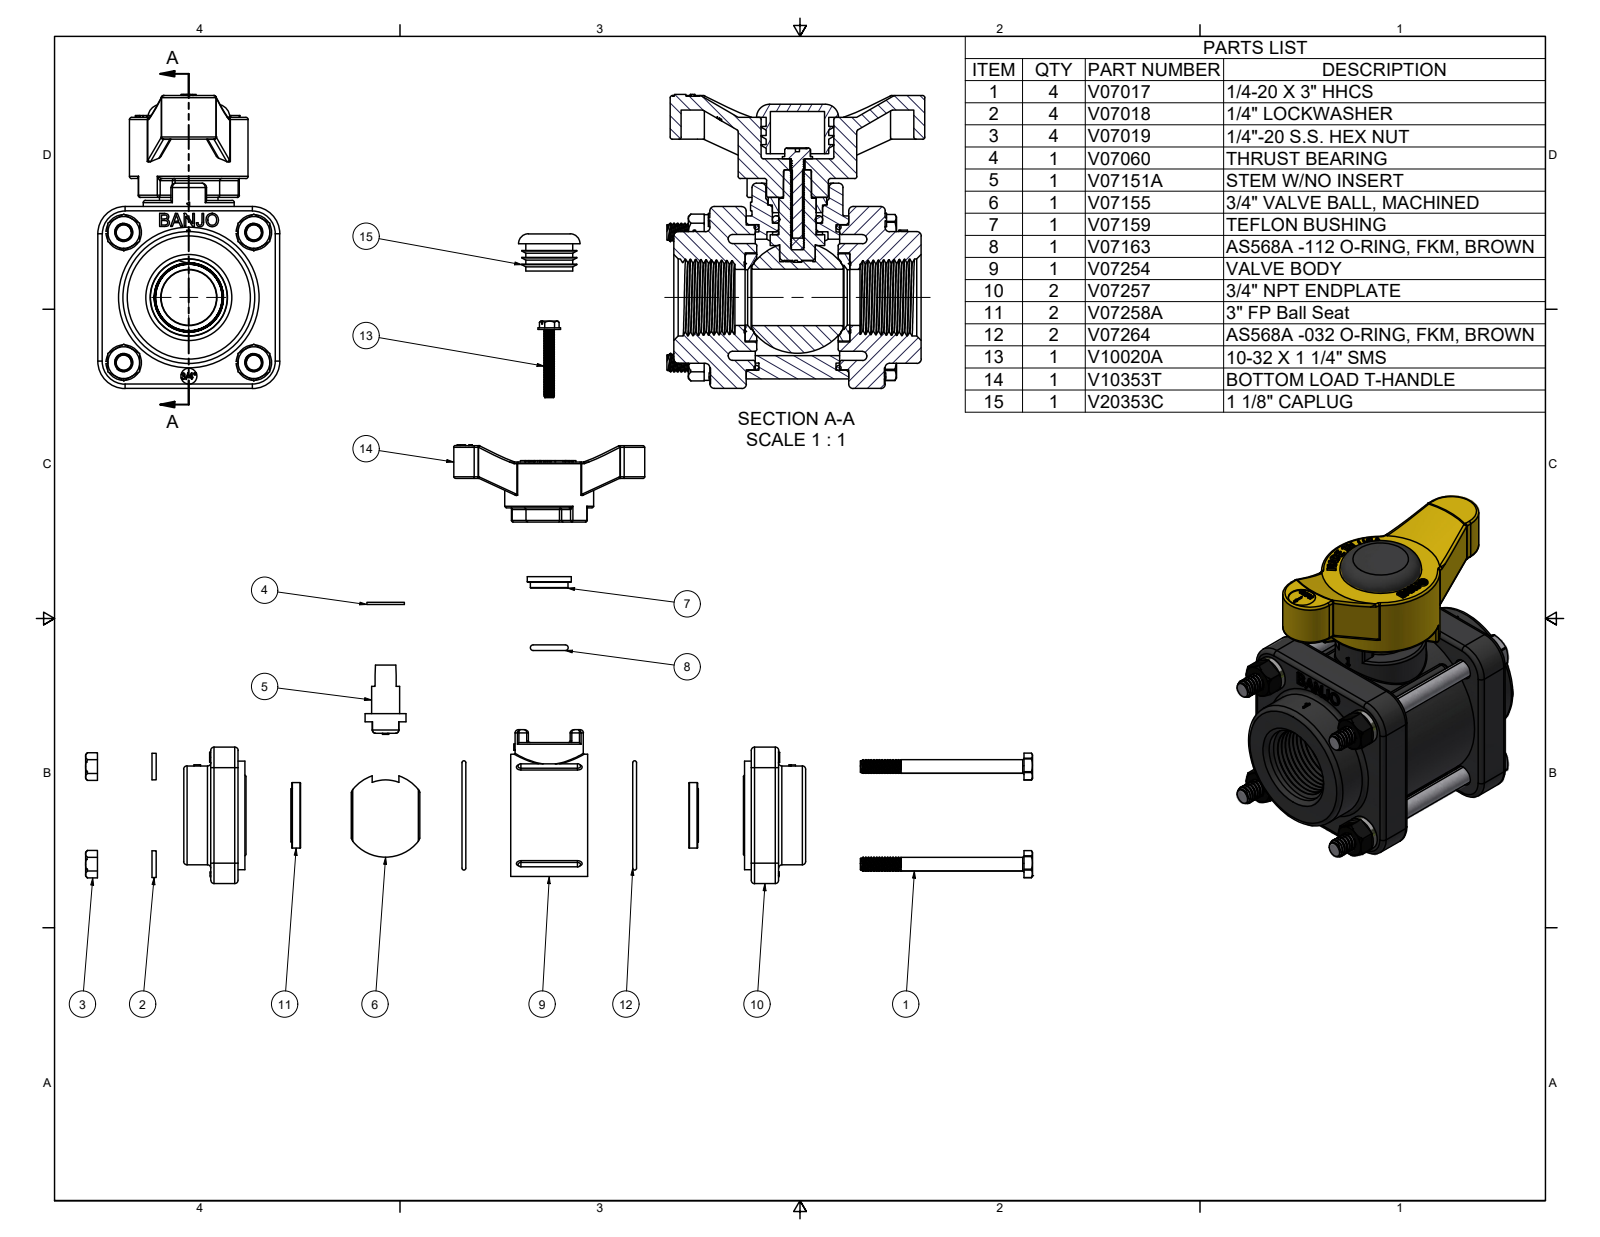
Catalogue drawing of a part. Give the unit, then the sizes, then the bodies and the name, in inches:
Units: inches
Overall size (bounding box): 4.04 × 3.545 × 2.5
Round holes (diameter × count): ⌀0.196 ×4, ⌀0.252 ×4, ⌀0.29 ×4, ⌀0.091 ×1, ⌀0.128 ×1, ⌀0.14 ×1, ⌀0.21 ×1, ⌀0.22 ×1, ⌀0.375 ×1, ⌀0.515 ×1, ⌀0.52 ×1, ⌀0.689 ×1
Round bosses / shafts (diameter × count): ⌀0.212 ×56, ⌀0.164 ×39, ⌀0.489 ×4, ⌀0.25 ×4, ⌀2.24 ×1, ⌀1.99 ×1, ⌀1.81 ×1, ⌀1.802 ×1
Partial cylindrical surfaces — rounded edges, fillets, slot ends (radius × count): R0.03 ×76, R0.06 ×24, R0.106 ×8, R0.375 ×6, R0.015 ×4, R0.248 ×4, R0.016 ×3, R0.013 ×2
Main face-to-face distances: 1.91, 0.5, 0.125, 1.41, 2.41, 2.5, 0.495, 0.995, 2.405, 2.905
Hole centre spacings: 1.265, 1.789, 0.913, 2.168, 2.53, 0.663, 1.08, 1.533
Volume: 14.28 in³ · Surface area: 149.9 in²
Bodies: 27 solids, 2468 faces (885 planar, 673 cylindrical, 910 other)
Part name (STEP PRODUCT): VT075; V07017; V07018; V07019 (+8 more)
STEP written by: Autodesk Inventor 2022 (AUTOMOTIVE_DESIGN)
